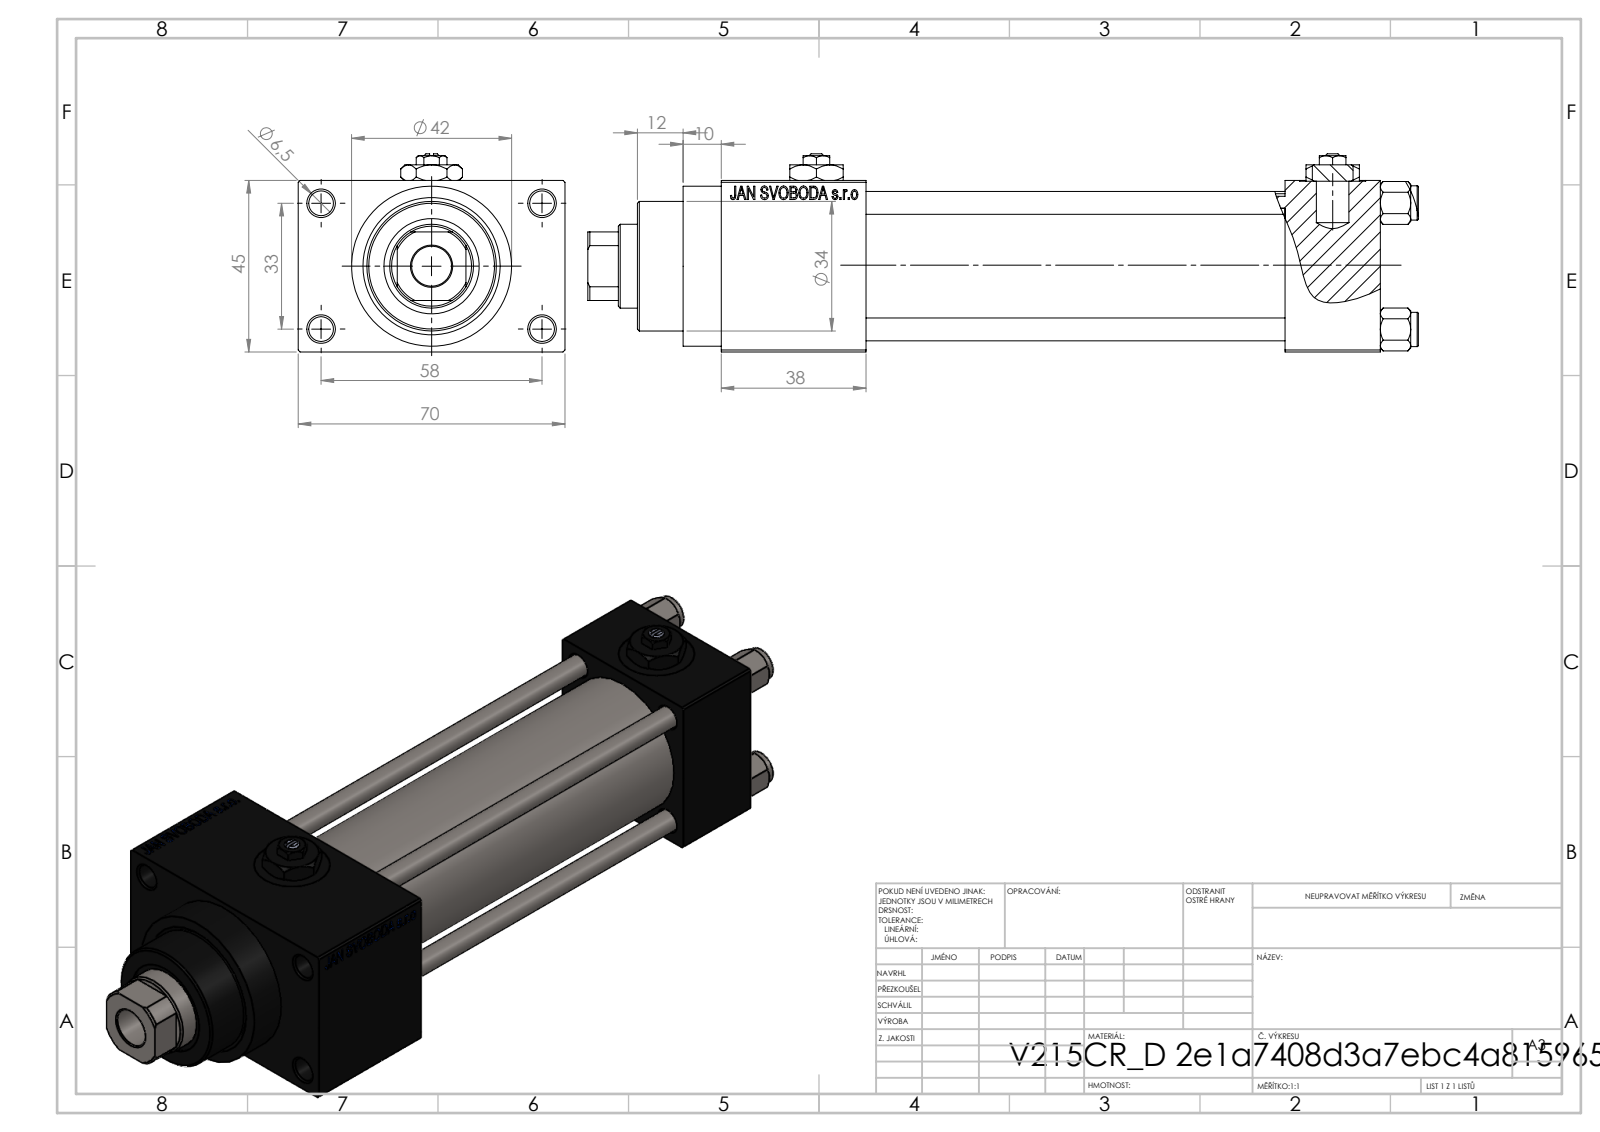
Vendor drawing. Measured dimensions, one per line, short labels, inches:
name: V215CR_VCP_D; Zatka_pro_OIL_PORT; V215_VC_A; NUT_M5_D (+2 more)
written by: SolidWorks 2019 (CONFIG_CONTROL_DESIGN)
unit: in
bodies: 13 solids, 1203 faces (542 planar, 99 cylindrical, 562 other)
size: 8.583 × 2.756 × 2.047
volume: 17.76 in³; area: 160.4 in²
holes: 4× ⌀0.236, 4× ⌀0.256, 4× ⌀0.518, 4× ⌀0.787, 3× ⌀0.276, 1× ⌀0.413, 1× ⌀0.866, 1× ⌀0.945, 1× ⌀0.984, 1× ⌀1.26, 1× ⌀1.299
bosses: 4× ⌀0.354, 1× ⌀1.654, 1× ⌀1.496, 1× ⌀1.339
rounds: 1× R0.413
face distances: 1.772, 0.984, 0.492, 4.331, 5.315, 2.264, 5.827, 1.496, 6.811, 2.756
hole spacings: 0.488, 0.924, 1.307, 1.314, 1.392, 1.795, 2.219, 1.299
